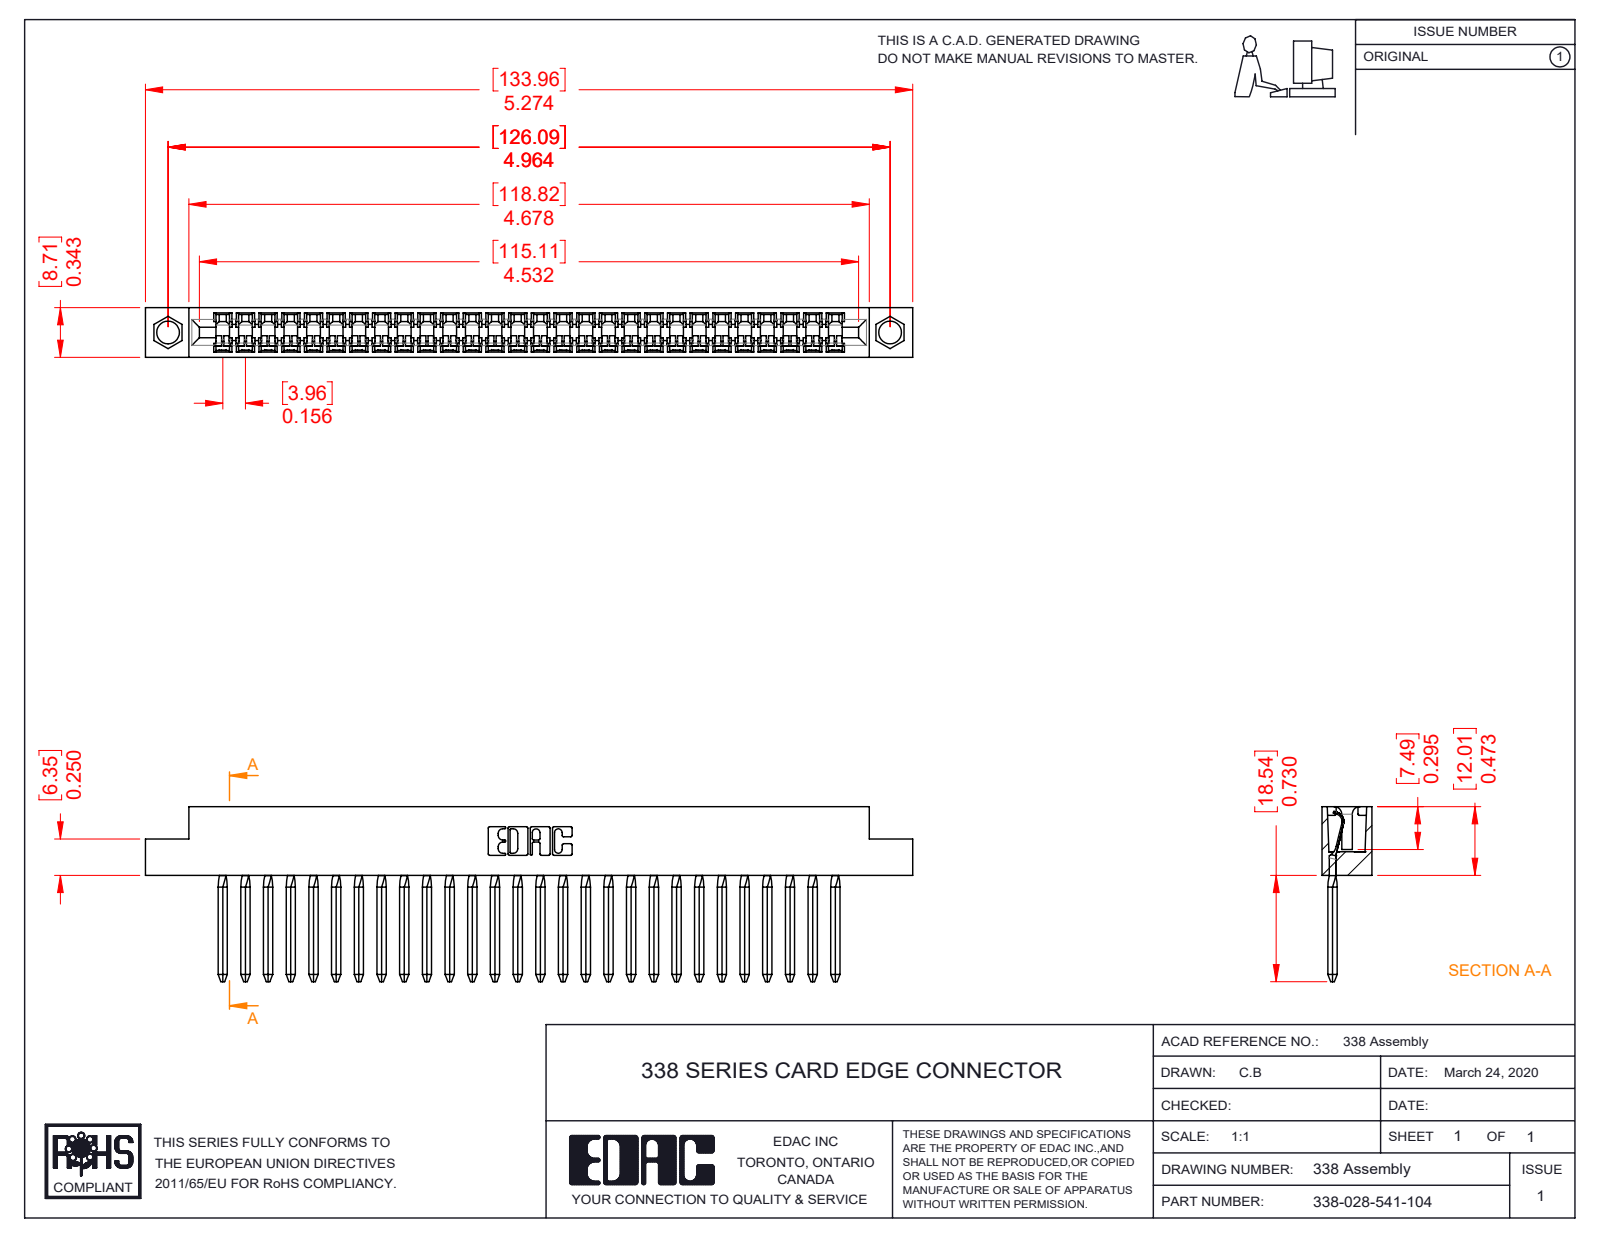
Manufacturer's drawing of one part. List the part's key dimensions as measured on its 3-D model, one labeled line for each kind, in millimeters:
Part name (STEP PRODUCT): 338-028-541-104; 338-290-001_541; 338-210-001_338-210-028-004
STEP written by: SolidWorks 2016 (CONFIG_CONTROL_DESIGN)
Units: millimetres
Bodies: 29 solids, 2712 faces (1884 planar, 716 cylindrical, 112 other)
Overall size (bounding box): 134 × 30.6 × 8.7
Volume: 9 290 mm³ · Surface area: 15 100 mm²
Round holes (diameter × count): ⌀4 ×2
Partial cylindrical surfaces — rounded edges, fillets, slot ends (radius × count): R0.6 ×114, R0.2 ×28, R1.4 ×23, R1.7 ×23, R0.3 ×22, R2.5 ×22, R0.2 ×6, R0.8 ×6
Main face-to-face distances: 8.7, 4, 2.8, 5.3, 3.4, 15.8, 19.8, 11.9, 1.2, 7.5
Hole centre spacings: 126.1
